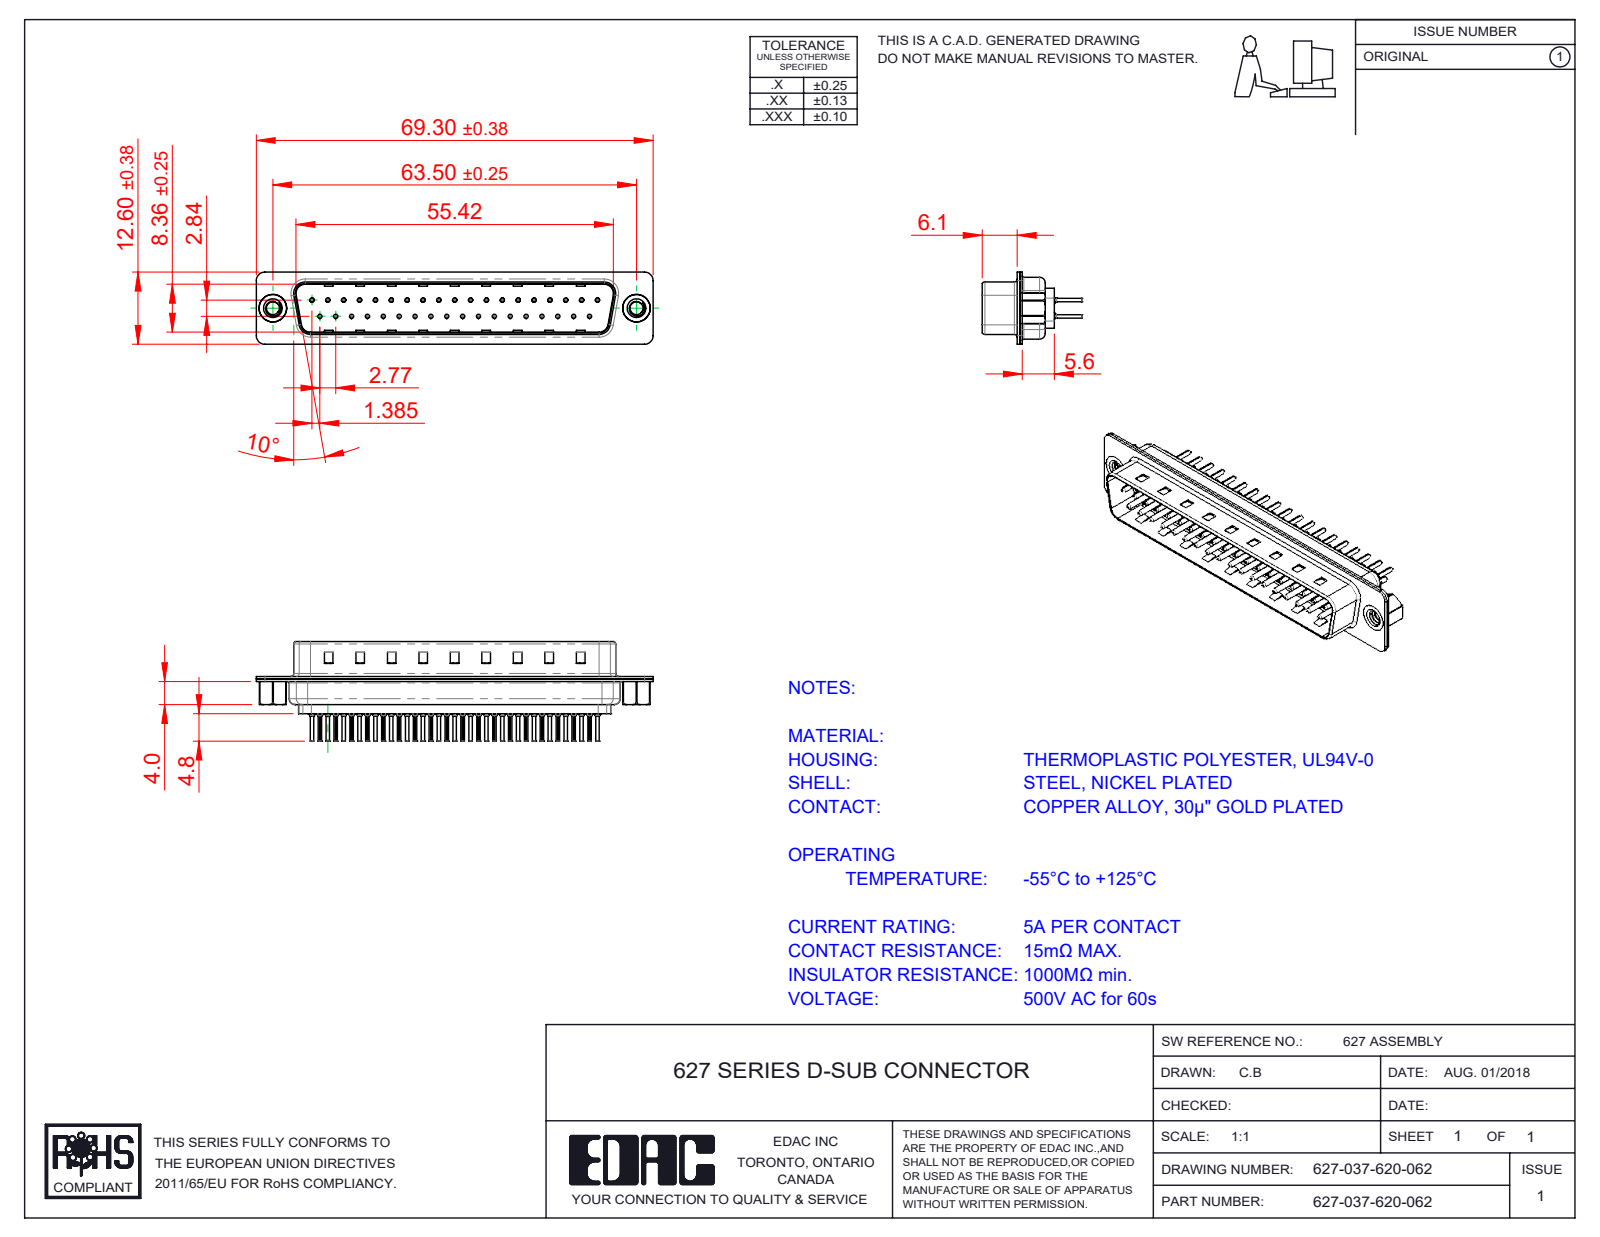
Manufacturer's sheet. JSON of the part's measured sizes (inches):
{"part_name": "627-037-620-062; 627 Shell Rear_37 Contacts; 627 Contact Row 2_20L; 627 Housing_37 LP (+3 more)", "step_written_by": "SolidWorks 2020 (CONFIG_CONTROL_DESIGN)", "units": "inches", "bodies": {"solids": 42, "faces": 4034, "planar": 1091, "cylindrical": 1508, "other": 1435}, "overall_size": [2.728, 0.681, 0.496], "volume_in3": 0.226, "surface_area_in2": 16.54, "round_holes": [[0.008, 37], [0.014, 37], [0.043, 37], [0.063, 37], [0.089, 2], [0.157, 2], [0.189, 2]], "round_bosses_or_shafts": [[0.079, 37], [0.059, 37], [0.03, 37], [0.024, 37], [0.197, 2], [0.193, 2]], "partial_cylinders_radius": [[0.004, 74], [0.059, 16], [0.079, 12], [0.02, 8], [0.063, 8], [0.01, 4], [0.024, 4], [0.026, 4]], "face_to_face_distances": [0.016, 0.032, 0.377, 0.018, 0.345, 0.059, 0.035, 0.055, 0.238, 0.017], "hole_center_spacings": [0.124, 0.109, 0.218, 0.327, 0.198, 0.398, 0.436, 0.503]}
